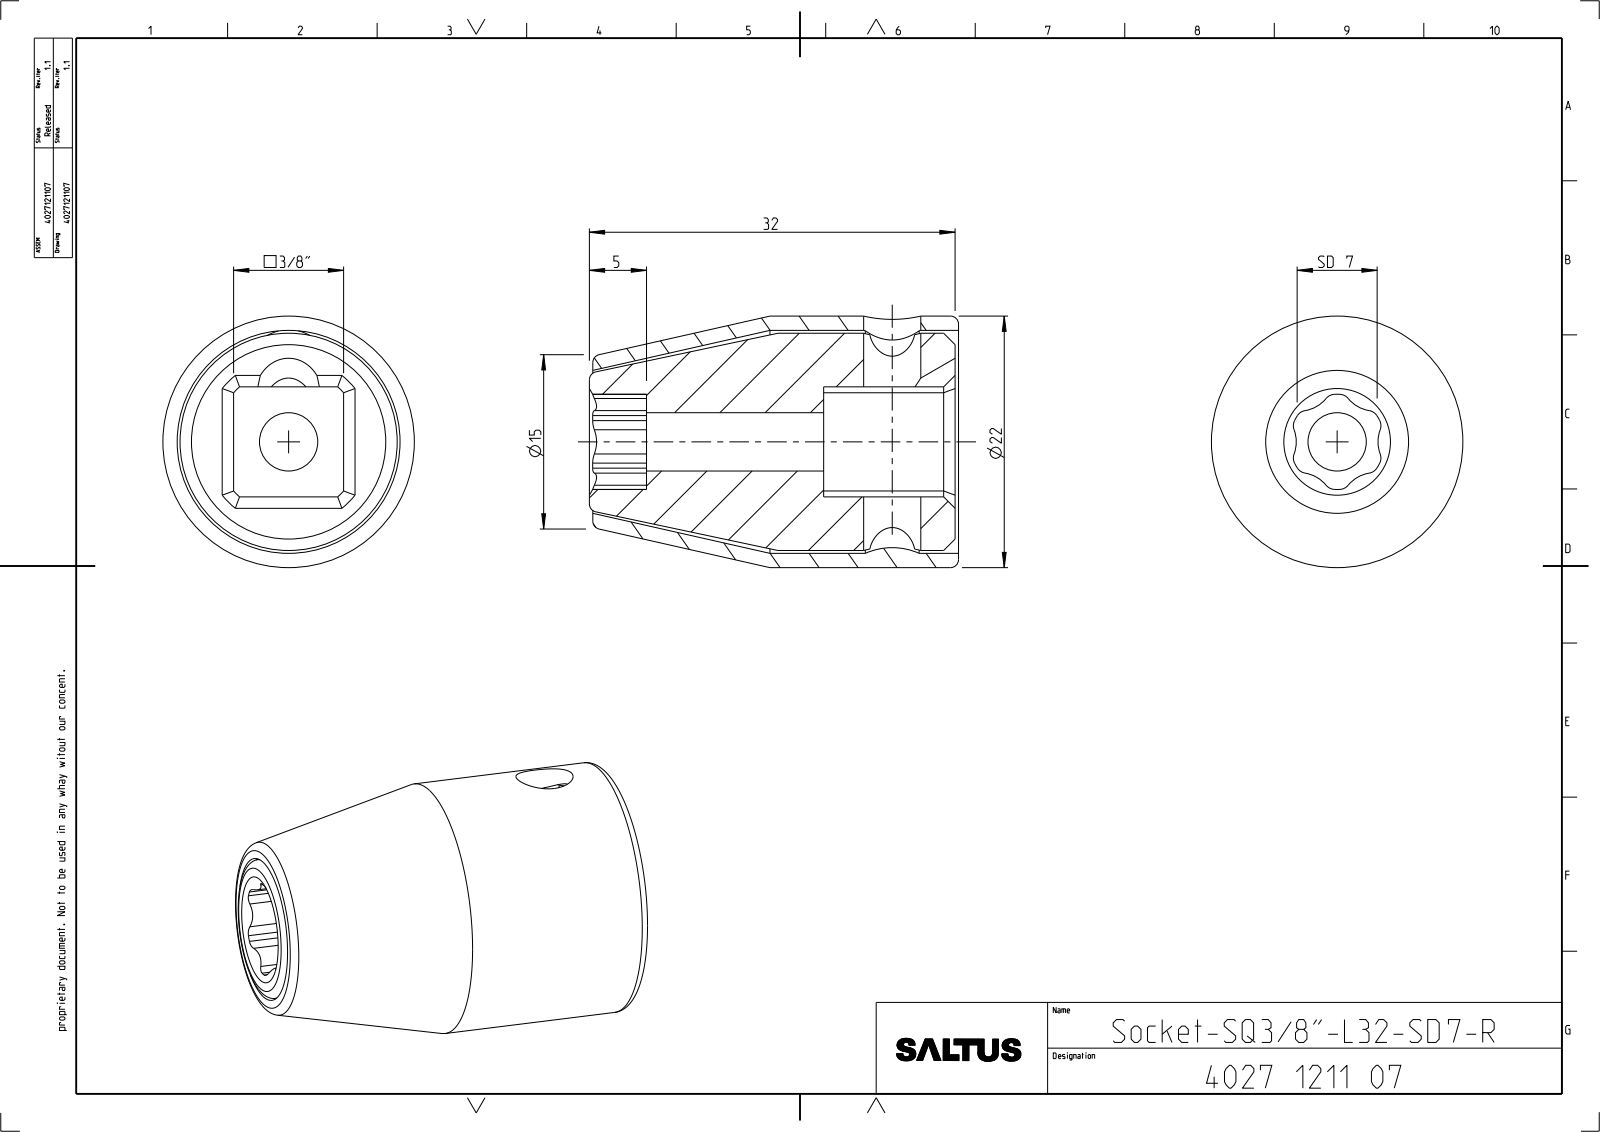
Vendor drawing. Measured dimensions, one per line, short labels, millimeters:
name: 4027120807; 4027036005; 4027121107_ASM
written by: CREO PARAMETRIC BY PTC INC, 2022414 (CONFIG_CONTROL_DESIGN)
unit: mm
bodies: 2 solids, 85 faces (15 planar, 47 cylindrical, 23 other)
size: 32.3 × 22 × 22
volume: 7 926 mm³; area: 6 883 mm²
holes: 1× ⌀5, 1× ⌀5.1, 1× ⌀19.5
bosses: 1× ⌀22, 1× ⌀19
rounds: 12× R1, 7× R3, 1× R4.17, 1× R6.45
face distances: 9.62, 11.5, 32, 11.8, 31.7, 20.2, 27.3, 27, 15.5, 4.7
